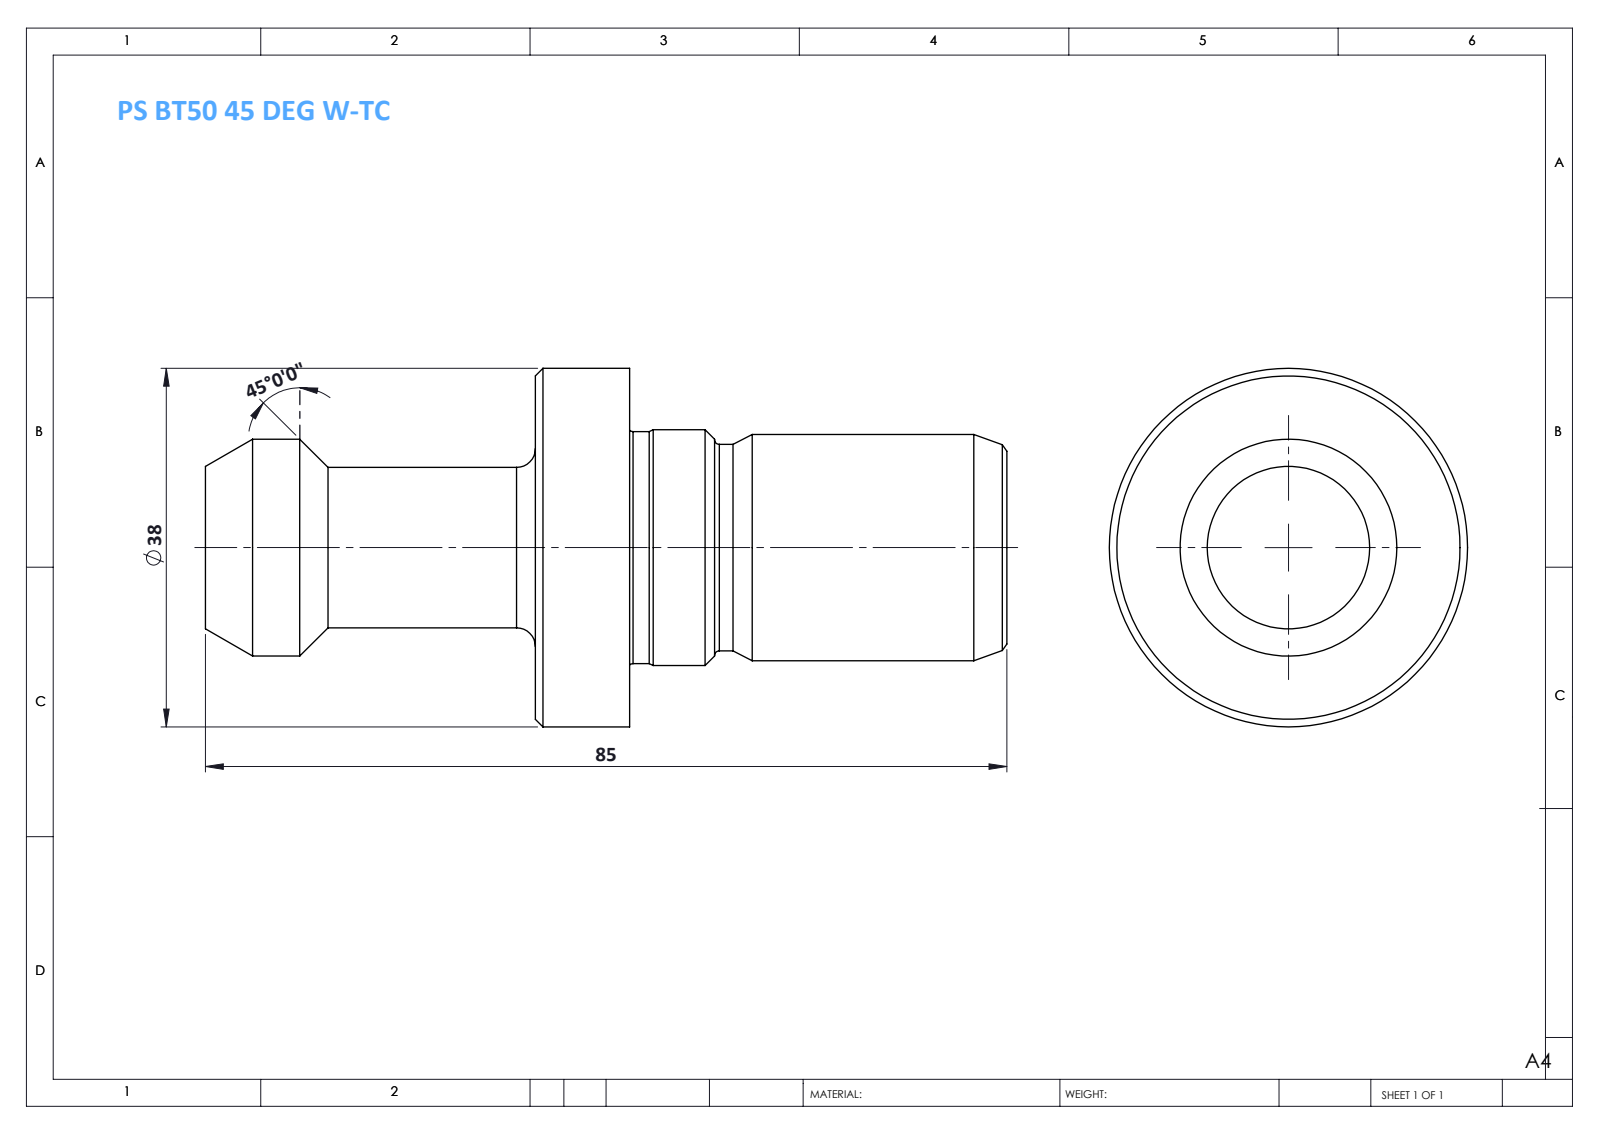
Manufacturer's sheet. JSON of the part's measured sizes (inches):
{"part_name": "PS BT50 45 DEG W-TC", "step_written_by": "SolidWorks 2014 (CONFIG_CONTROL_DESIGN)", "units": "inches", "bodies": {"solids": 1, "faces": 43, "planar": 5, "cylindrical": 14, "other": 24}, "overall_size": [3.346, 1.496, 1.496], "volume_in3": 2.376, "surface_area_in2": 13.18, "round_bosses_or_shafts": [[1.496, 1], [0.984, 1], [0.969, 1], [0.945, 1], [0.906, 1], [0.862, 1], [0.669, 1]], "face_to_face_distances": [0.394, 1.575, 1.969, 3.346, 1.772, 1.378, 1.22, 0.354, 0.748, 2.126]}
